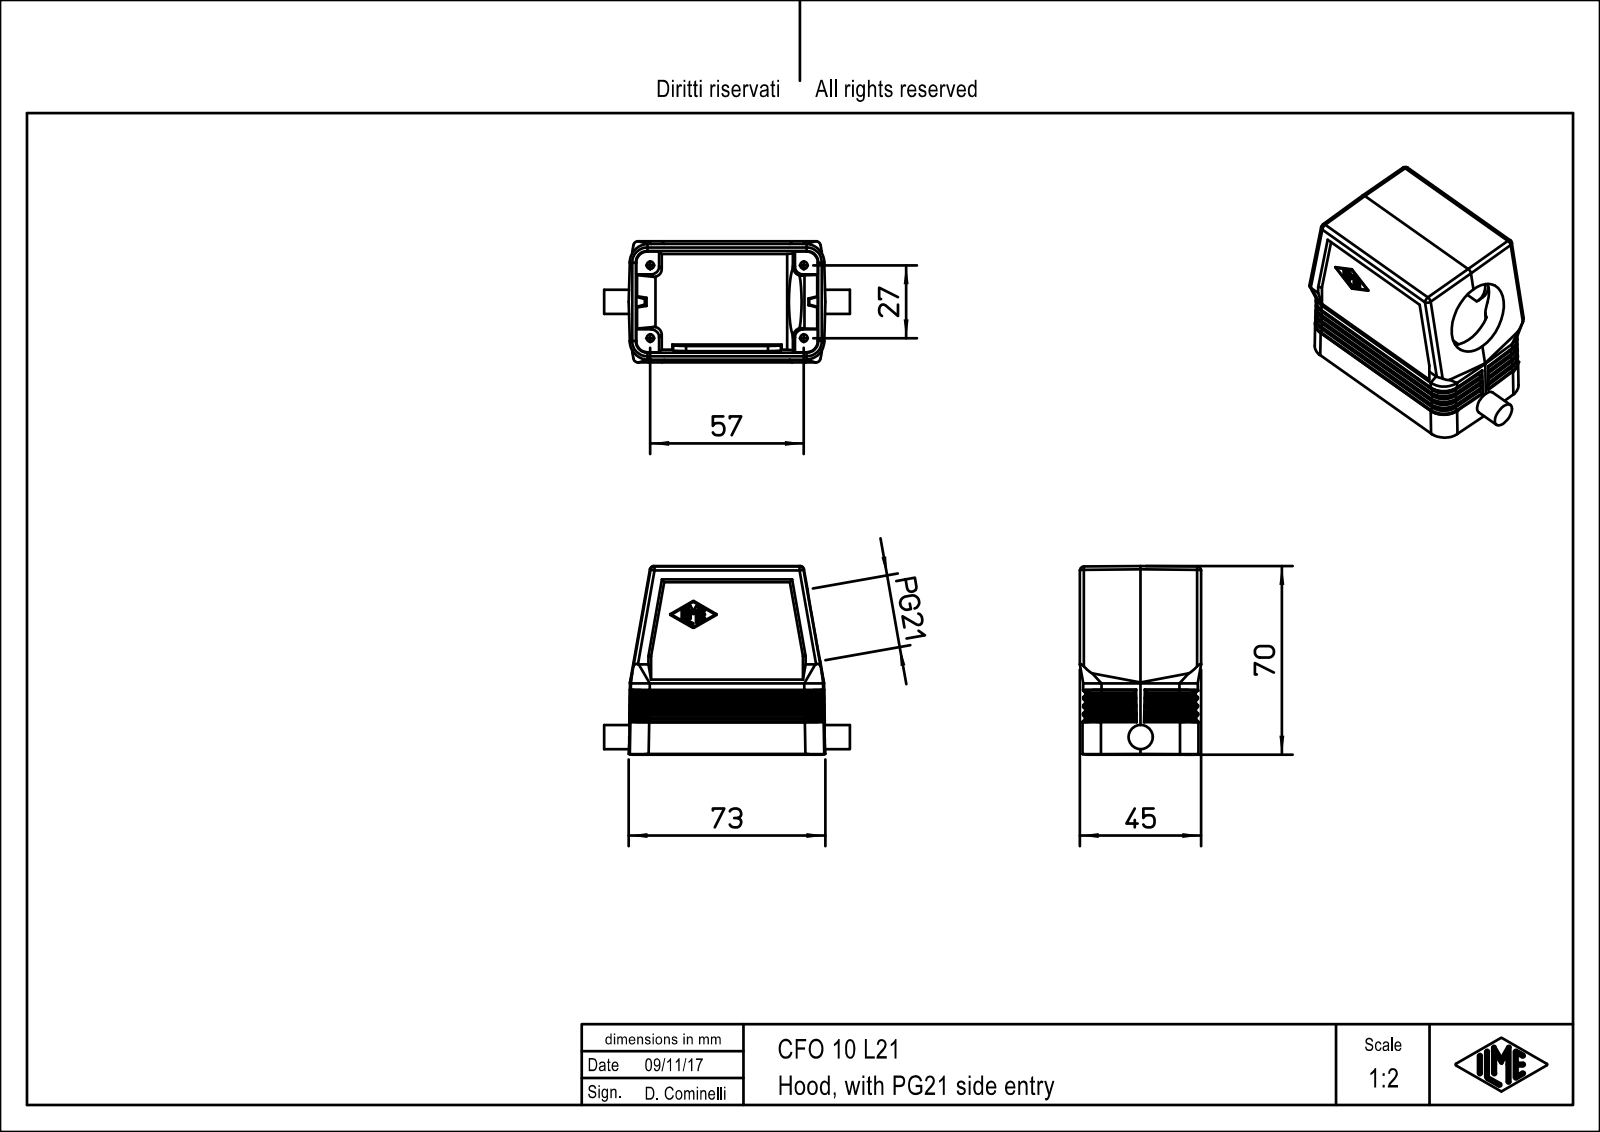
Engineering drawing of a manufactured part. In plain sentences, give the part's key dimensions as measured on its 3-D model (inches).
The part is named "CFO_10_L21". Its 3-D file was written by "PTC Creo Elements/Direct Modeling 19.0E 27-Jun-2016 (C) Parametric Technology GmbH (AUTOMOTIVE_DESIGN)". It is 1 solid with 340 faces: 140 planar, 66 cylindrical and 134 other. Overall it measures 3.59 by 2.756 by 1.772 inches. Its volume is 4.114 cubic inches and its surface area 51.9 square inches. Round holes: 4 of diameter 0.108, 1 of diameter 0.189, 1 of diameter 1.063. Round bosses or shafts: 1 of diameter 0.354, 1 of diameter 0.126. Partial cylindrical surfaces (rounded edges, fillets, slot ends): 16 of radius 0.02, 10 of radius 0.059, 8 of radius 0.276, 4 of radius 0.118, 4 of radius 0.165, 1 of radius 0.787. The main face-to-face distances are 1.693, 0.335, 0.075, 0.079, 1.732, 0.039, 0.157, 1.772, 0.236, 0.447. The hole center spacings are 1.063, 2.244, 2.483.
